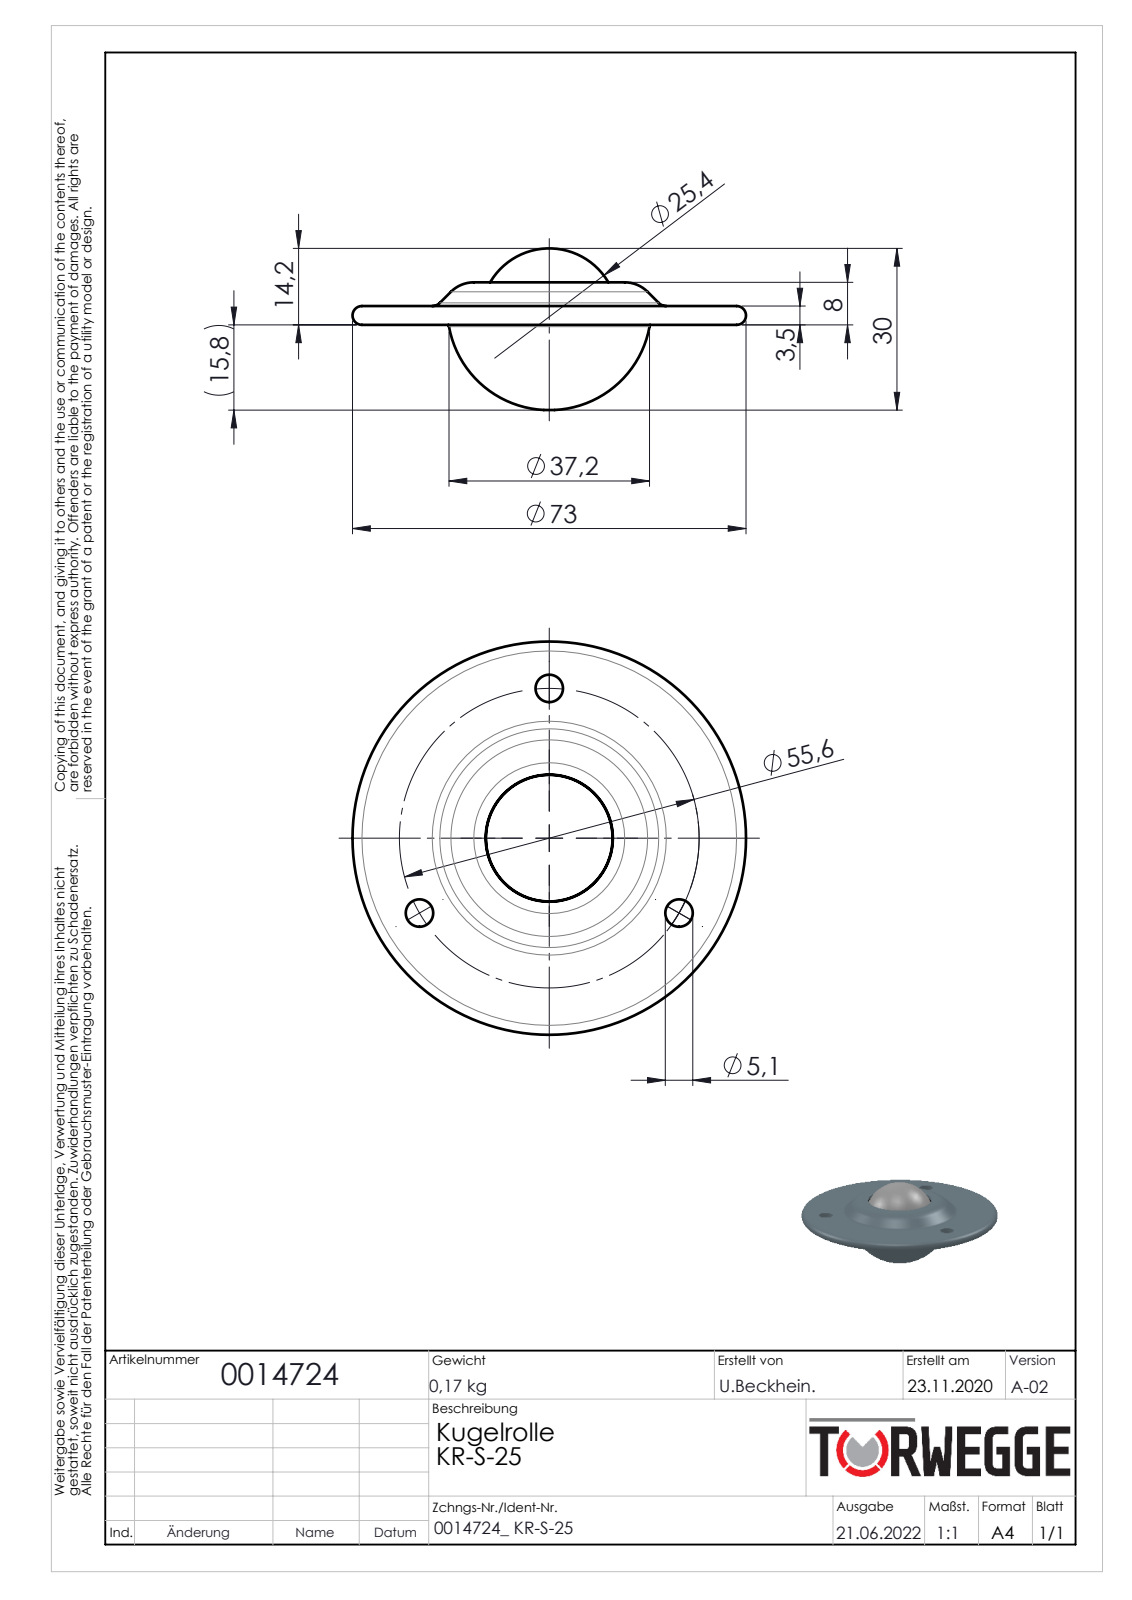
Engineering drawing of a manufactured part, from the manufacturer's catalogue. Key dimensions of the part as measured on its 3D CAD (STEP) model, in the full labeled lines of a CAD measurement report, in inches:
Part name (STEP PRODUCT): 0014724
STEP written by: SolidWorks 2020 (AUTOMOTIVE_DESIGN)
Units: inches
Bodies: 1 solid, 38 faces (6 planar, 14 cylindrical, 18 other)
Overall size (bounding box): 2.874 × 2.874 × 1.181
Volume: 1.771 in³ · Surface area: 16.12 in²
Round holes (diameter × count): ⌀0.201 ×3, ⌀0.079 ×1, ⌀0.929 ×1, ⌀0.971 ×1, ⌀2.551 ×1
Main face-to-face distances: 0.102, 0.035, 0.138, 0.311, 0.276, 0.173, 0.249, 0.213, 0.111, 0.062
Hole centre spacings: 1.094, 1.896, 1.896
